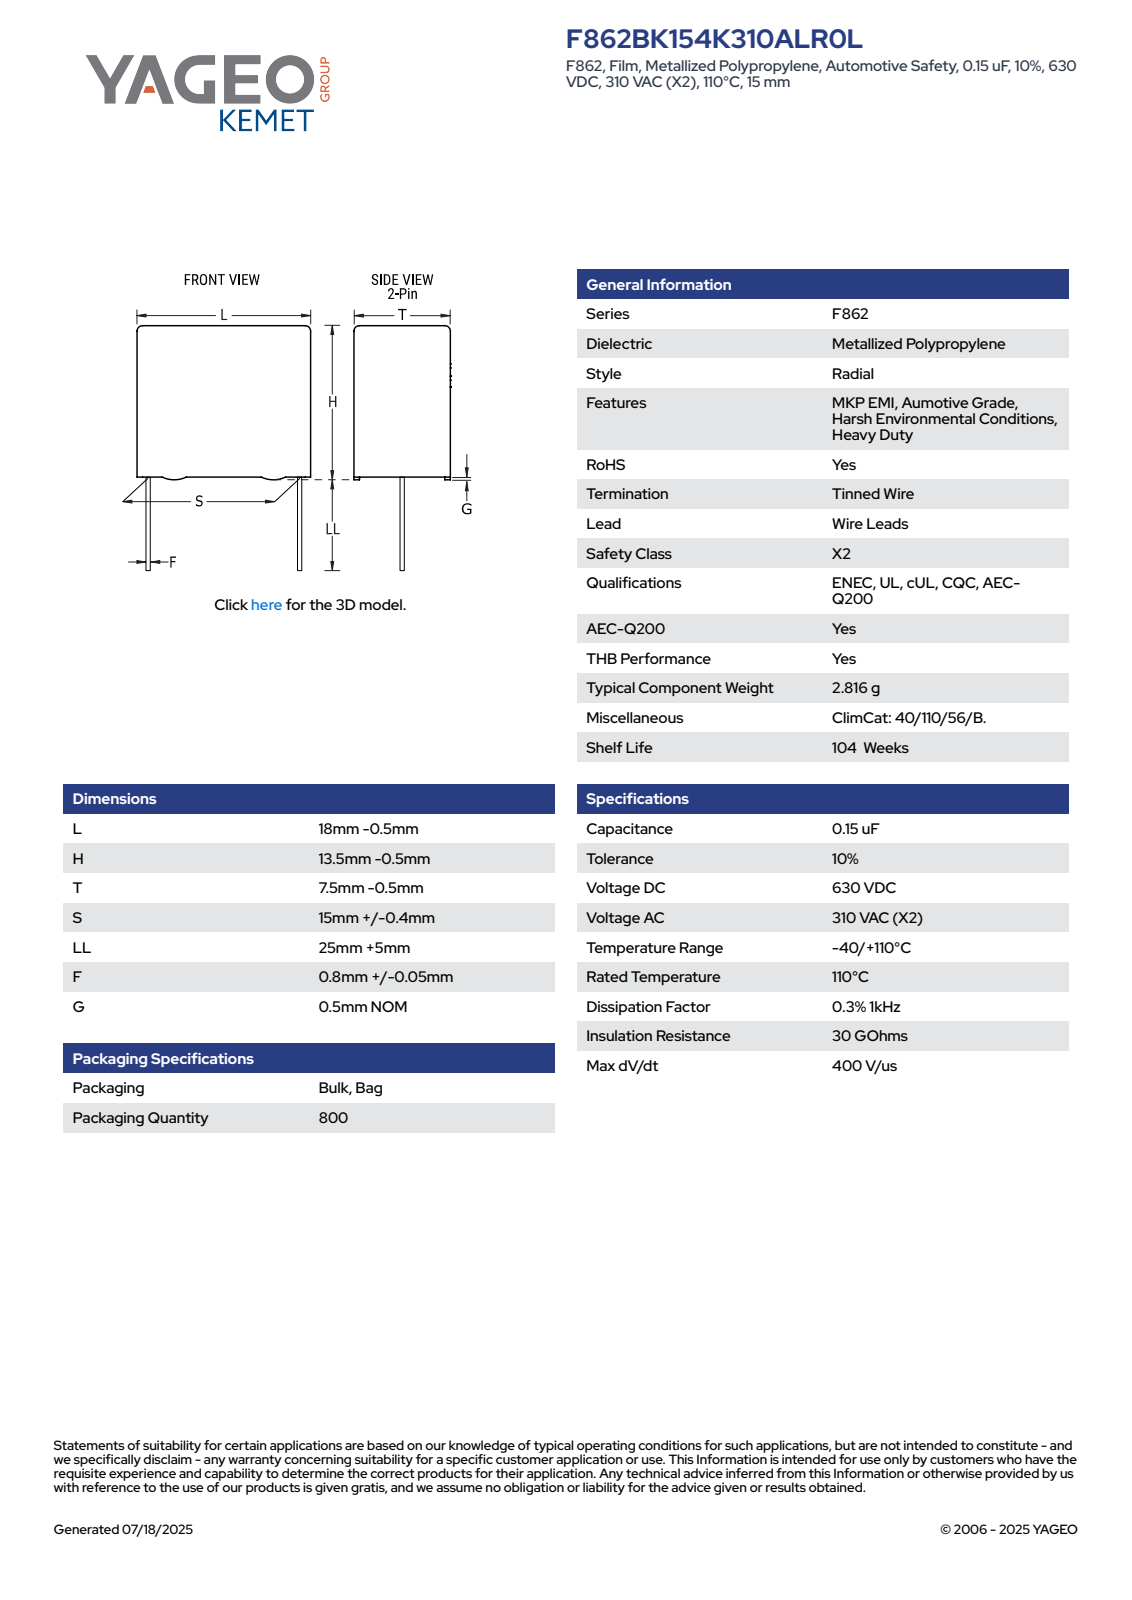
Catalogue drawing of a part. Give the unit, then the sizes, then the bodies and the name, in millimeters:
Units: millimetres
Overall size (bounding box): 43 × 17.5 × 7
Round bosses / shafts (diameter × count): ⌀0.85 ×2
Partial cylindrical surfaces — rounded edges, fillets, slot ends (radius × count): R0.5 ×4
Main face-to-face distances: 7, 12.5, 17.5, 6.6, 0.4, 0.5, 13, 6.2, 30, 30.5
Volume: 1 566 mm³ · Surface area: 1 055 mm²
Bodies: 4 solids, 89 faces (81 planar, 8 cylindrical, 0 other)
Part name (STEP PRODUCT): CFR_RBG_18X13.5X7.5_L17.5H13T7S15LL30F0.85G0.5
STEP written by: SolidWorks 2014 (AUTOMOTIVE_DESIGN)
